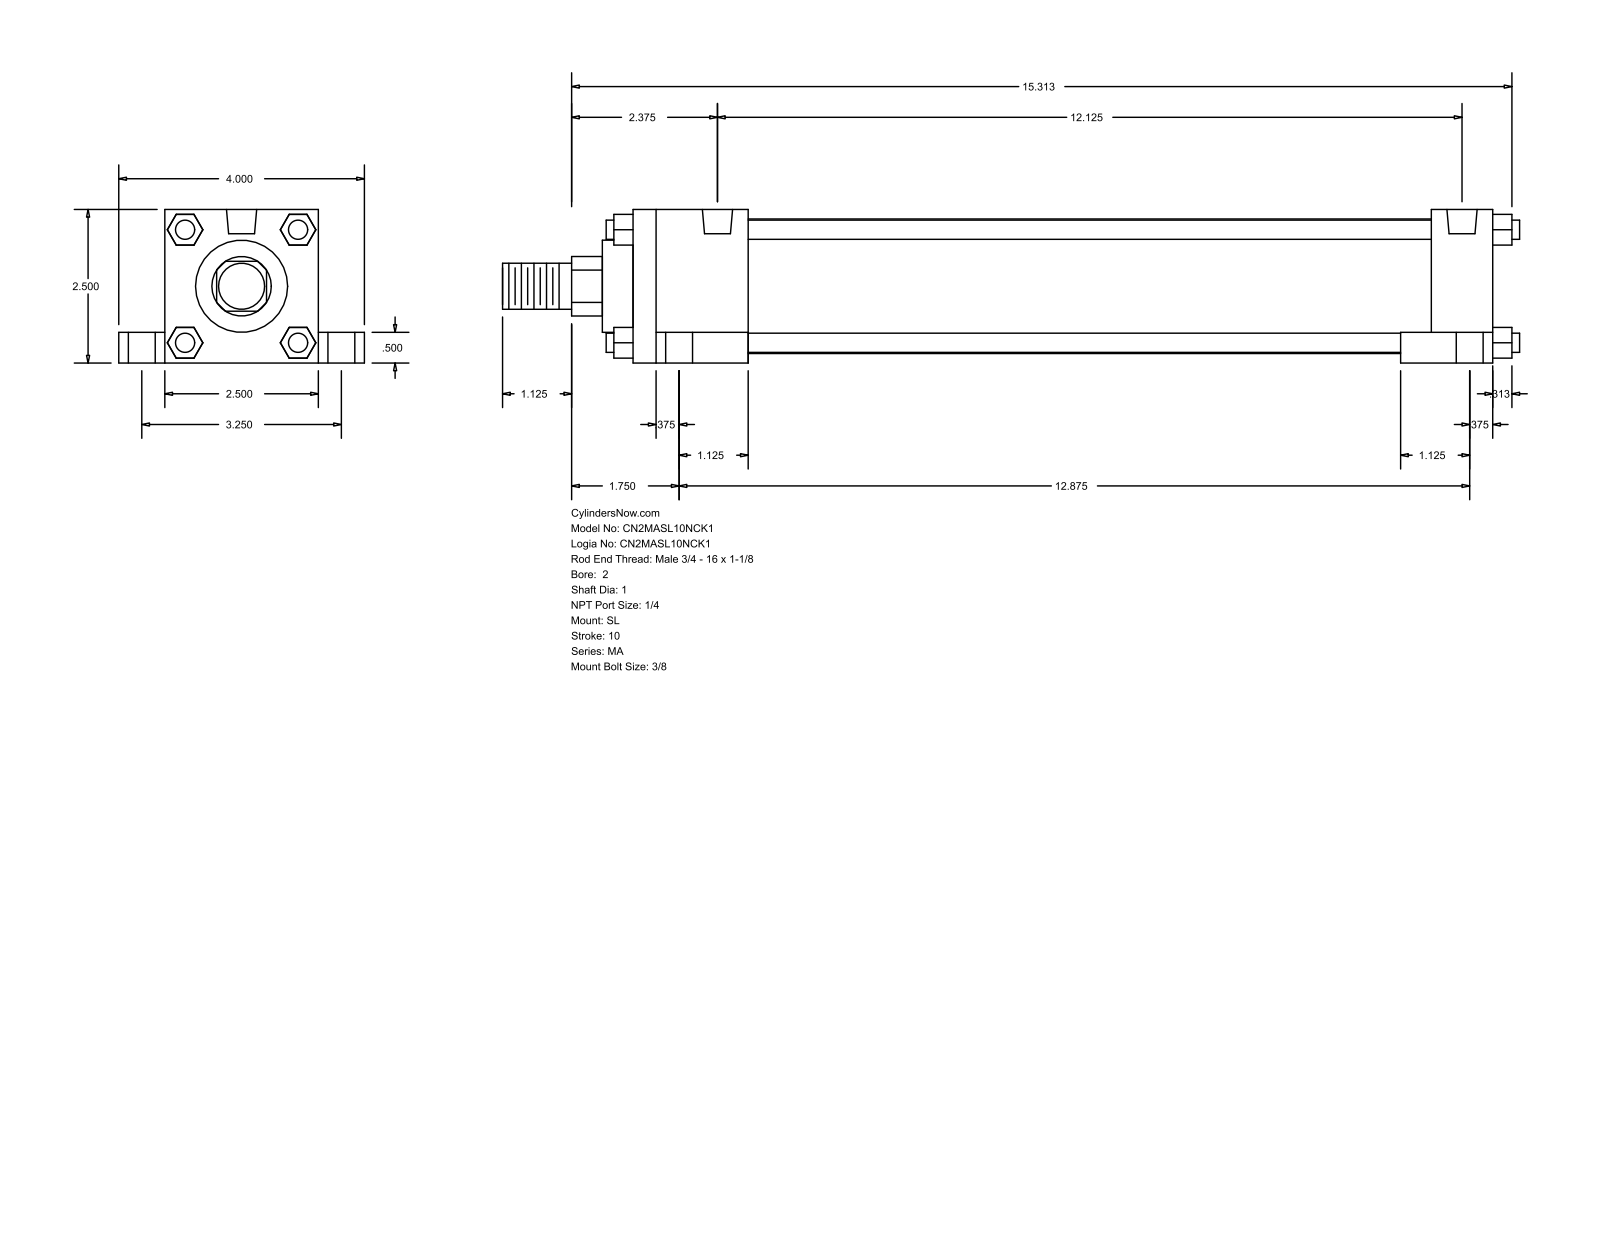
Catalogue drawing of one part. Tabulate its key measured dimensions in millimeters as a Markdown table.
| quantity | value |
| --- | --- |
| part name | MA_SL__0200_1 |
| STEP written by | GSSL Pune (CONFIG_CONTROL_DESIGN) |
| units | millimeters |
| bodies | 0 solids, 148 faces (112 planar, 36 cylindrical, 0 other) |
| overall size | 420.69 × 101.6 × 63.5 |
| round holes (diameter × count) | 7.94 × 4, 11.11 × 4, 17.46 × 4, 12.49 × 2 |
| round bosses / shafts (diameter × count) | 7.94 × 4, 55.63 × 1, 38.1 × 1, 25.4 × 1, 19.05 × 1 |
| partial cylindrical surfaces (radius × count) | 12.29 × 1 |
| main face-to-face distances | 63.5, 12.7, 355.6, 19.05, 82.55, 25.4, 50.8, 47.63, 307.97, 330.2 |
| hole center spacings | 41.39, 44.22, 82.54, 307.97, 313.88, 326.47, 327.03, 337.29 |
